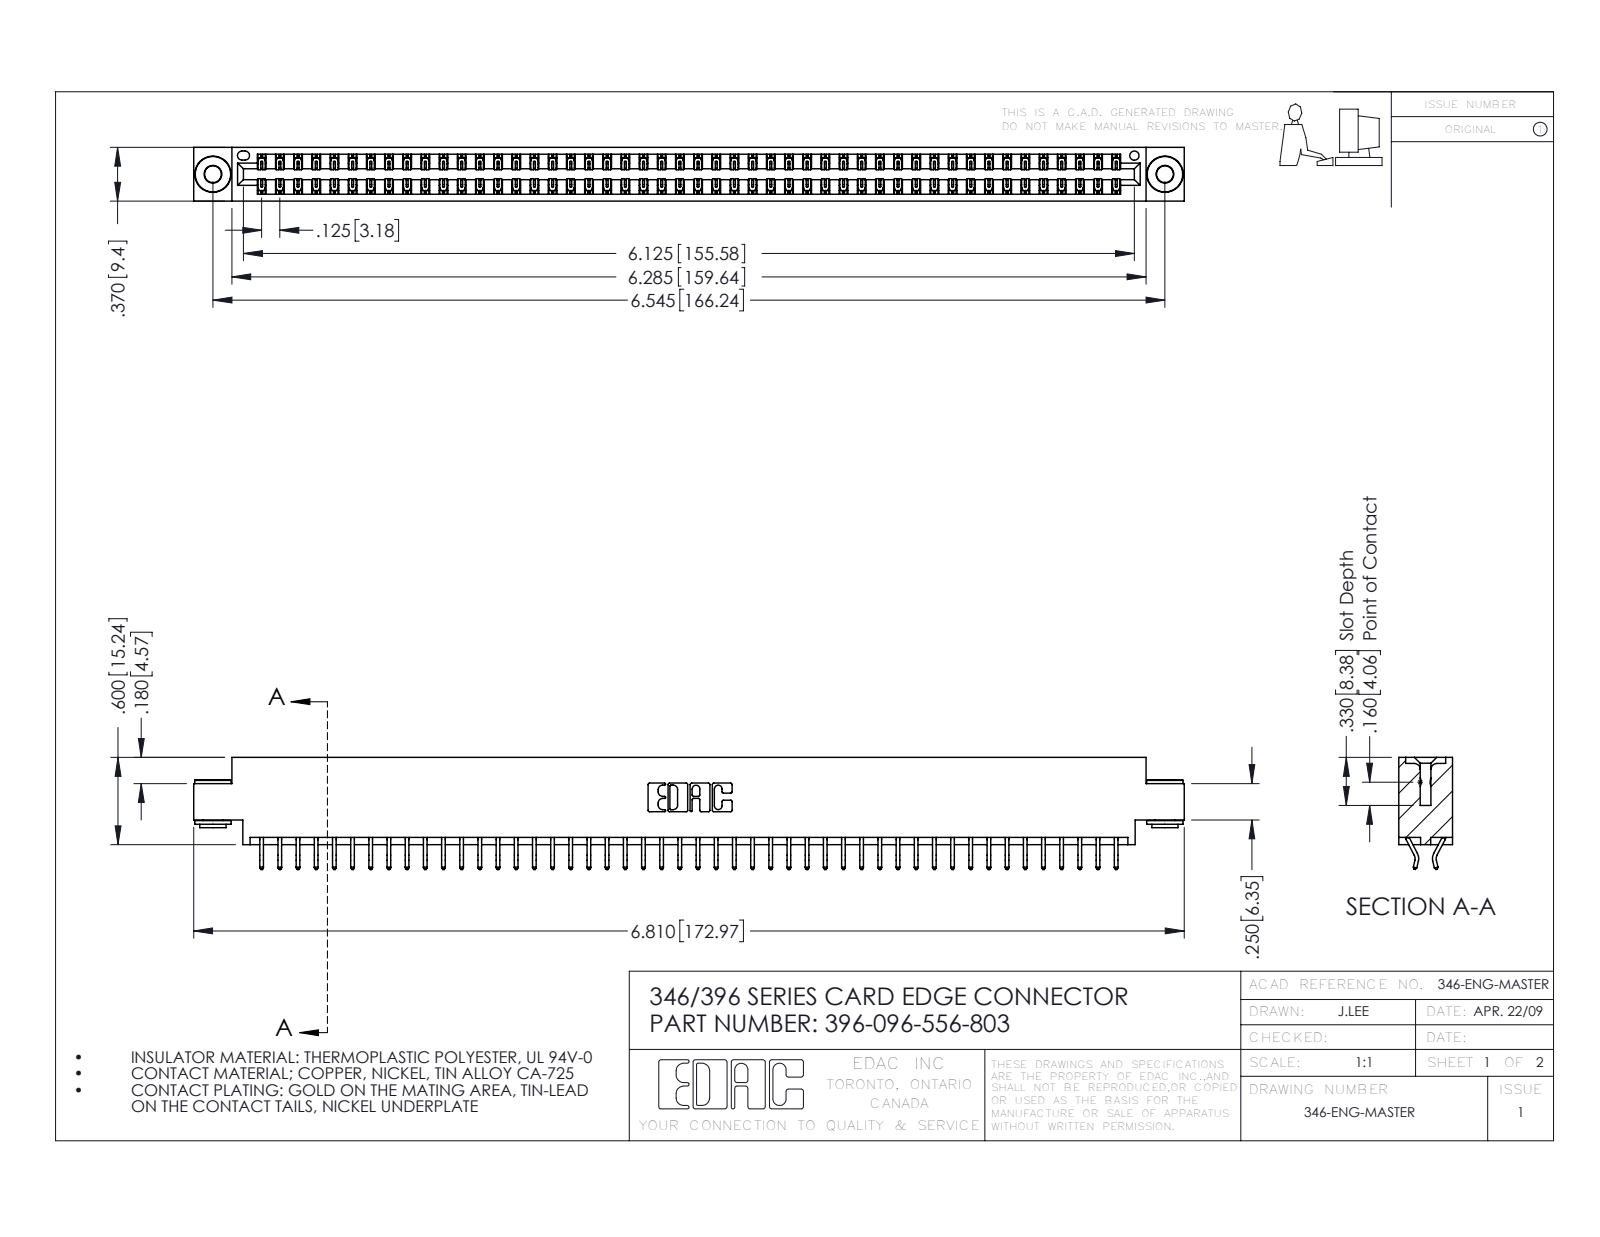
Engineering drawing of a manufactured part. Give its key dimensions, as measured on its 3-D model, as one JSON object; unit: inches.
{"part_name": "345-250-002_345-250-002-102; 396-096-556-803; 346 Part_0.170 Offset - 0.156 Dia-TH; 345-292-001_556 Tail", "step_written_by": "SolidWorks 2016 (CONFIG_CONTROL_DESIGN)", "units": "inches", "bodies": {"solids": 99, "faces": 5732, "planar": 3834, "cylindrical": 1890, "other": 8}, "overall_size": [6.81, 0.77, 0.37], "volume_in3": 1.024, "surface_area_in2": 36.36, "round_holes": [[0.116, 2], [0.156, 2], [0.064, 1]], "round_bosses_or_shafts": [[0.25, 2], [0.18, 2], [0.136, 2]], "partial_cylinders_radius": [[0.006, 144], [0.01, 22], [0.007, 6], [0.031, 6], [0.026, 3], [0.01, 2], [0.014, 2], [0.022, 2]], "face_to_face_distances": [0.048, 0.322, 0.37, 0.25, 0.025, 0.275, 0.072, 0.298, 0.148, 0.222], "hole_center_spacings": [0.246, 6.336, 6.545]}
